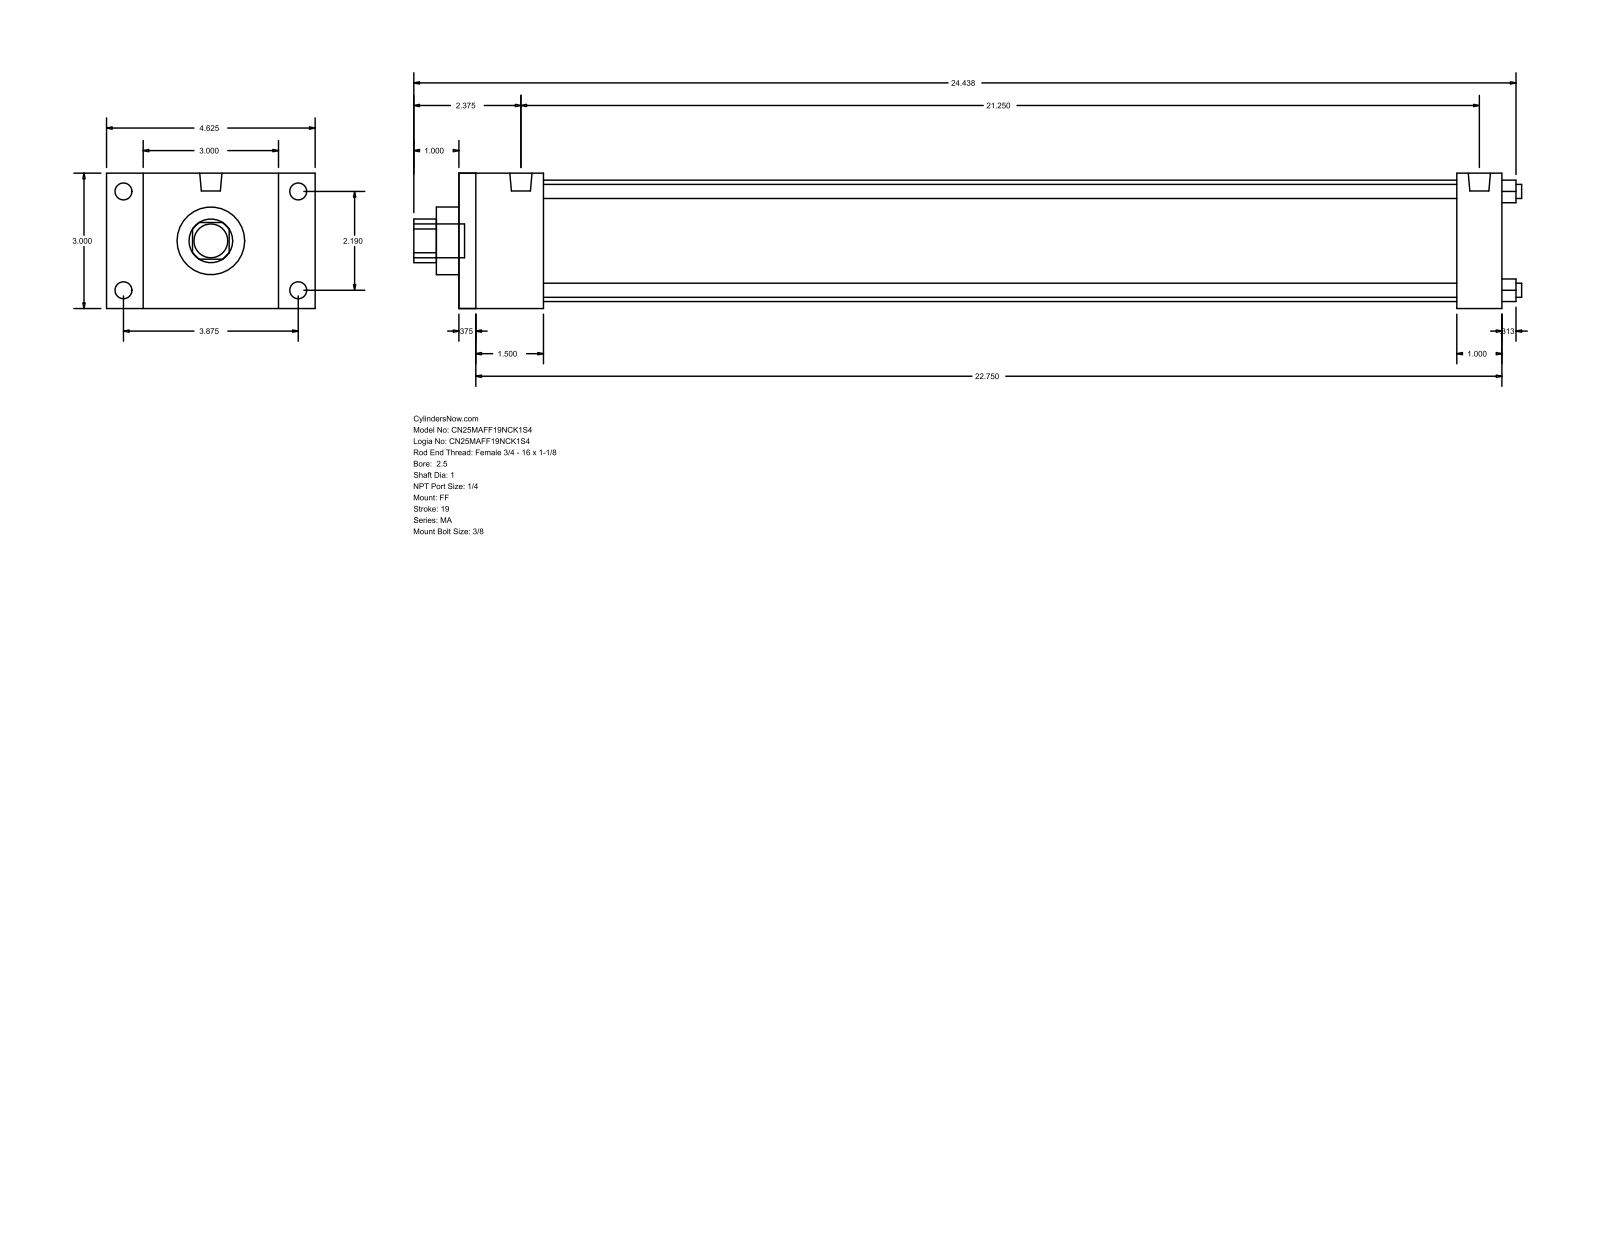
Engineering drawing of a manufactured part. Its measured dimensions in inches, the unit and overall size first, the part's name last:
Units: inches
Overall size (bounding box): 24.563 × 4.625 × 3
Round holes (diameter × count): ⌀0.313 ×4, ⌀1 ×1, ⌀1.5 ×1, ⌀2.69 ×1
Round bosses / shafts (diameter × count): ⌀0.375 ×4, ⌀0.313 ×4, ⌀0.492 ×2, ⌀0.75 ×1
Partial cylindrical surfaces — rounded edges, fillets, slot ends (radius × count): R0.484 ×1
Main face-to-face distances: 3, 23.125, 22.75, 0.375, 1, 1.875, 22.125, 1.5, 21.75, 20.25
Hole centre spacings: 1.548, 2.19, 3.097
Bodies: 0 solids, 92 faces (64 planar, 28 cylindrical, 0 other)
Part name (STEP PRODUCT): MA_FF__0250_1
STEP written by: GSSL Pune (CONFIG_CONTROL_DESIGN)
